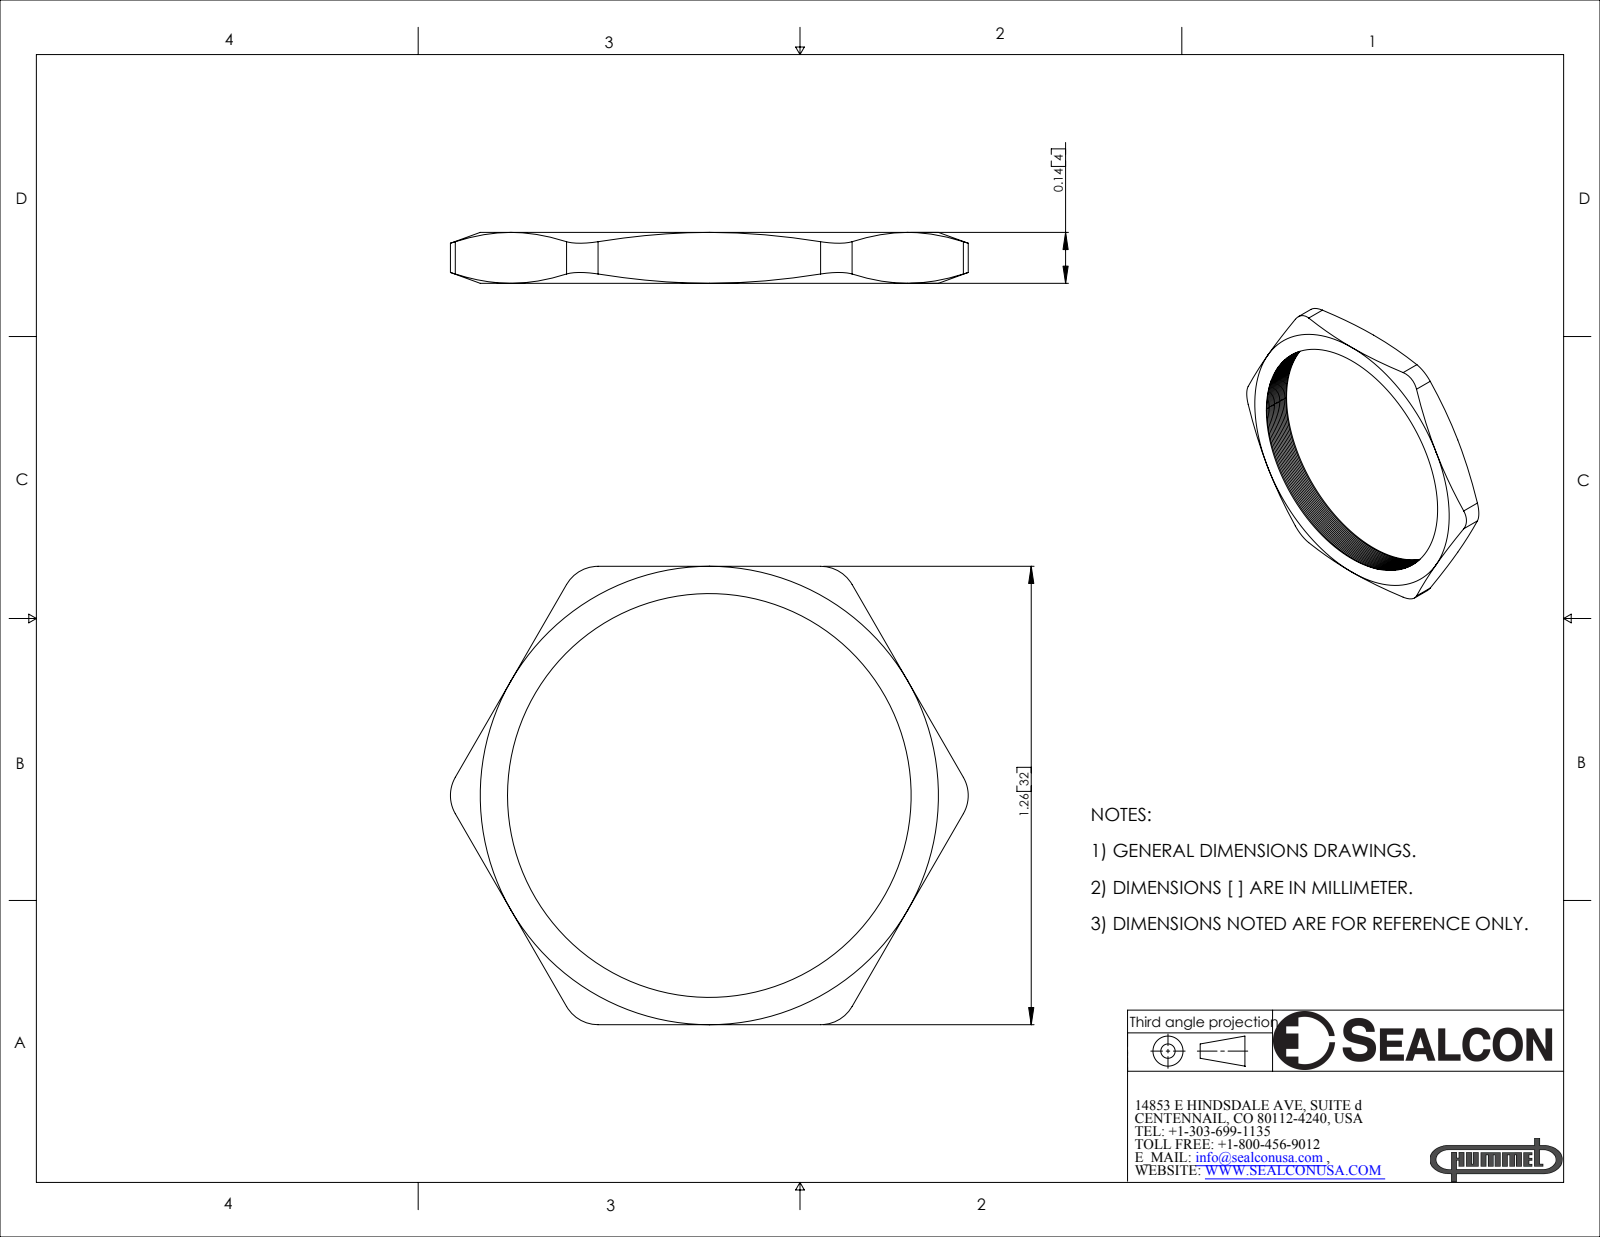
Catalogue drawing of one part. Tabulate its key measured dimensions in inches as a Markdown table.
| quantity | value |
| --- | --- |
| part name | NP-21-BR |
| STEP written by | SolidWorks 2007 (CONFIG_CONTROL_DESIGN) |
| units | inches |
| bodies | 1 solid, 97 faces (8 planar, 7 cylindrical, 82 other) |
| overall size | 1.424 × 1.26 × 0.14 |
| volume | 0.048 in³ |
| surface area | 2.29 in² |
| partial cylindrical surfaces (radius × count) | 0.1 × 6 |
| main face-to-face distances | 0.14, 1.26 |
